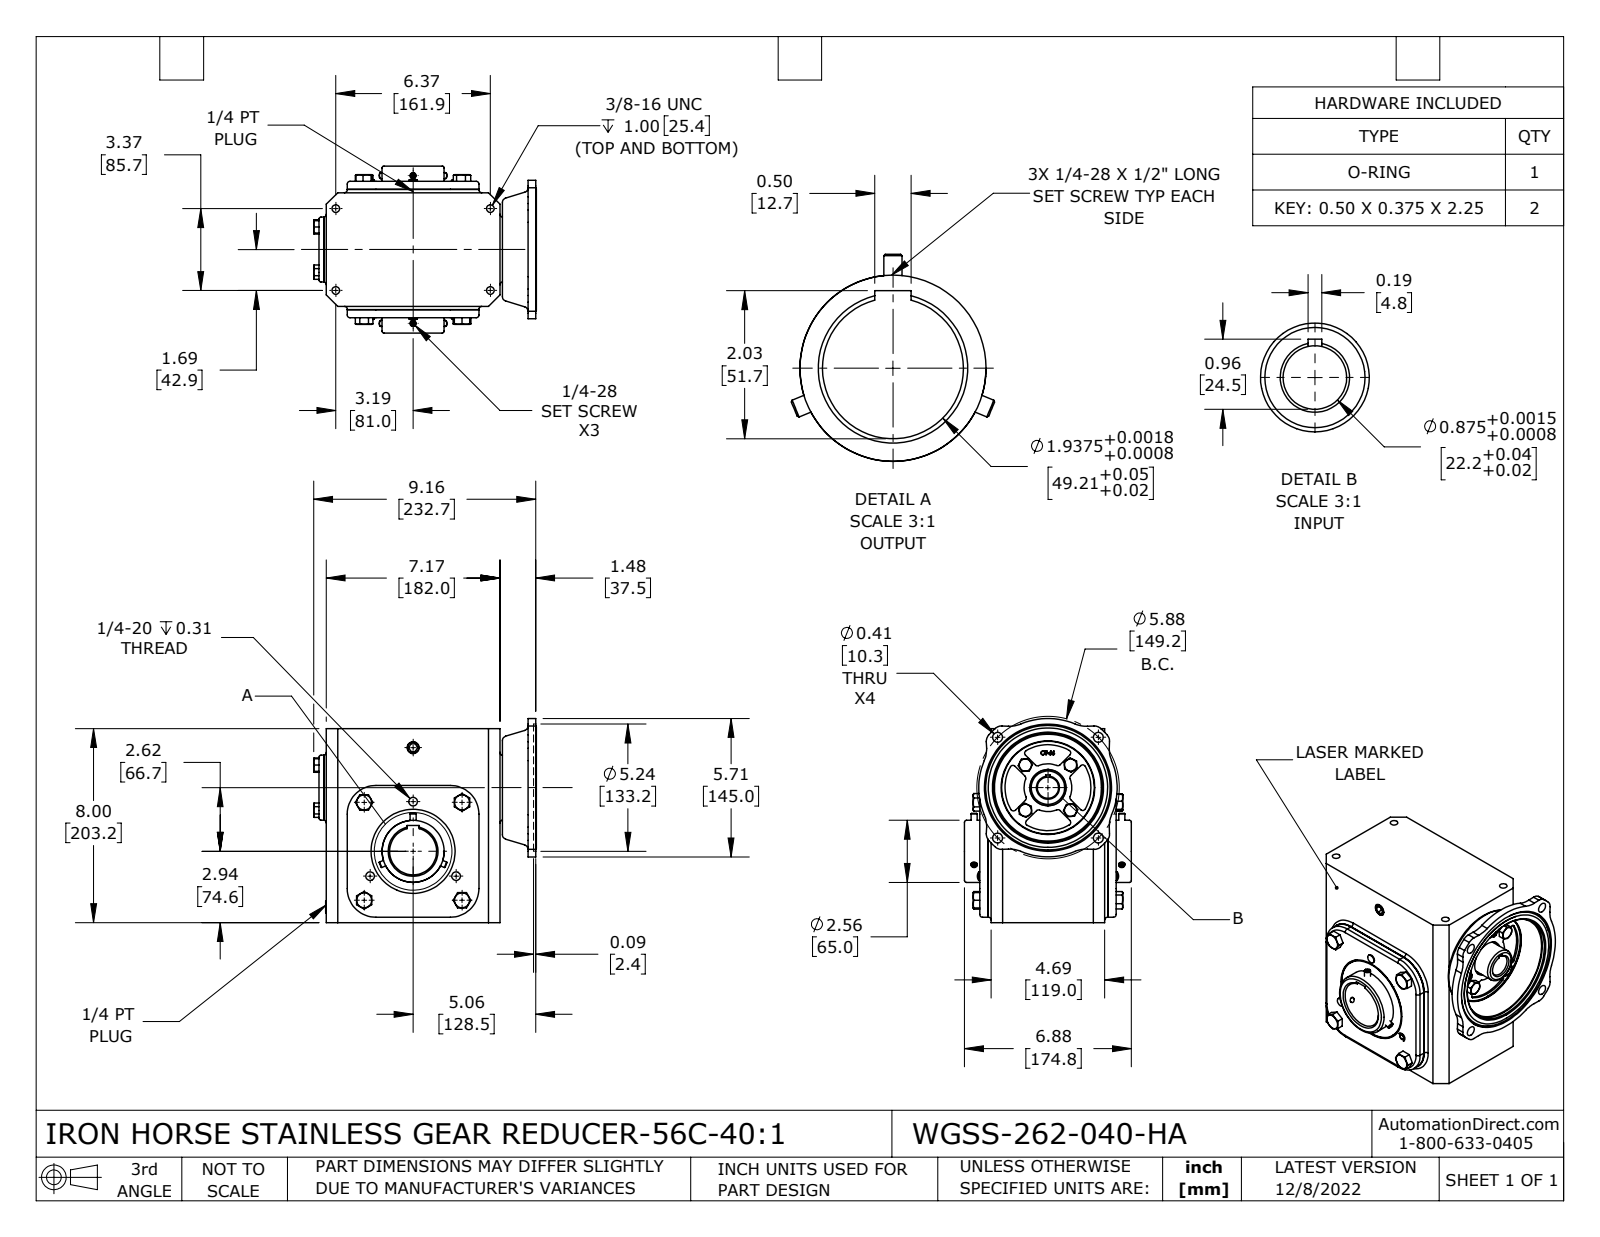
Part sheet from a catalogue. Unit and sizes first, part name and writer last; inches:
Units: inches
Overall size (bounding box): 9.184 × 8.417 × 6.882
Round holes (diameter × count): ⌀0.213 ×6, ⌀0.268 ×4, ⌀0.313 ×4, ⌀0.335 ×4, ⌀0.354 ×4, ⌀0.406 ×4, ⌀0.433 ×4, ⌀0.201 ×3, ⌀0.079 ×2, ⌀0.875 ×1, ⌀0.941 ×1, ⌀1.102 ×1
Round bosses / shafts (diameter × count): ⌀0.25 ×6, ⌀0.709 ×4, ⌀0.394 ×4, ⌀0.315 ×4, ⌀0.354 ×3, ⌀0.205 ×3, ⌀4.921 ×1, ⌀4.409 ×1
Partial cylindrical surfaces — rounded edges, fillets, slot ends (radius × count): R0.118 ×40, R0.394 ×12, R1.181 ×12, R0.039 ×8, R0.197 ×8, R0.079 ×6, R0.236 ×4, R0.019 ×2
Main face-to-face distances: 0.197, 0.335, 4.961, 0.669, 7.803, 0.472, 5.157, 4.488, 0.138, 6.969
Hole centre spacings: 3.22, 1.319, 1.619, 1.865, 2.855, 2.937, 3.465, 4.037
Volume: 121.8 in³ · Surface area: 1 055 in²
Bodies: 45 solids, 1776 faces (625 planar, 516 cylindrical, 635 other)
Part name (STEP PRODUCT): WGSS-262-040-HA
STEP written by: SolidWorks 2021 (CONFIG_CONTROL_DESIGN)
